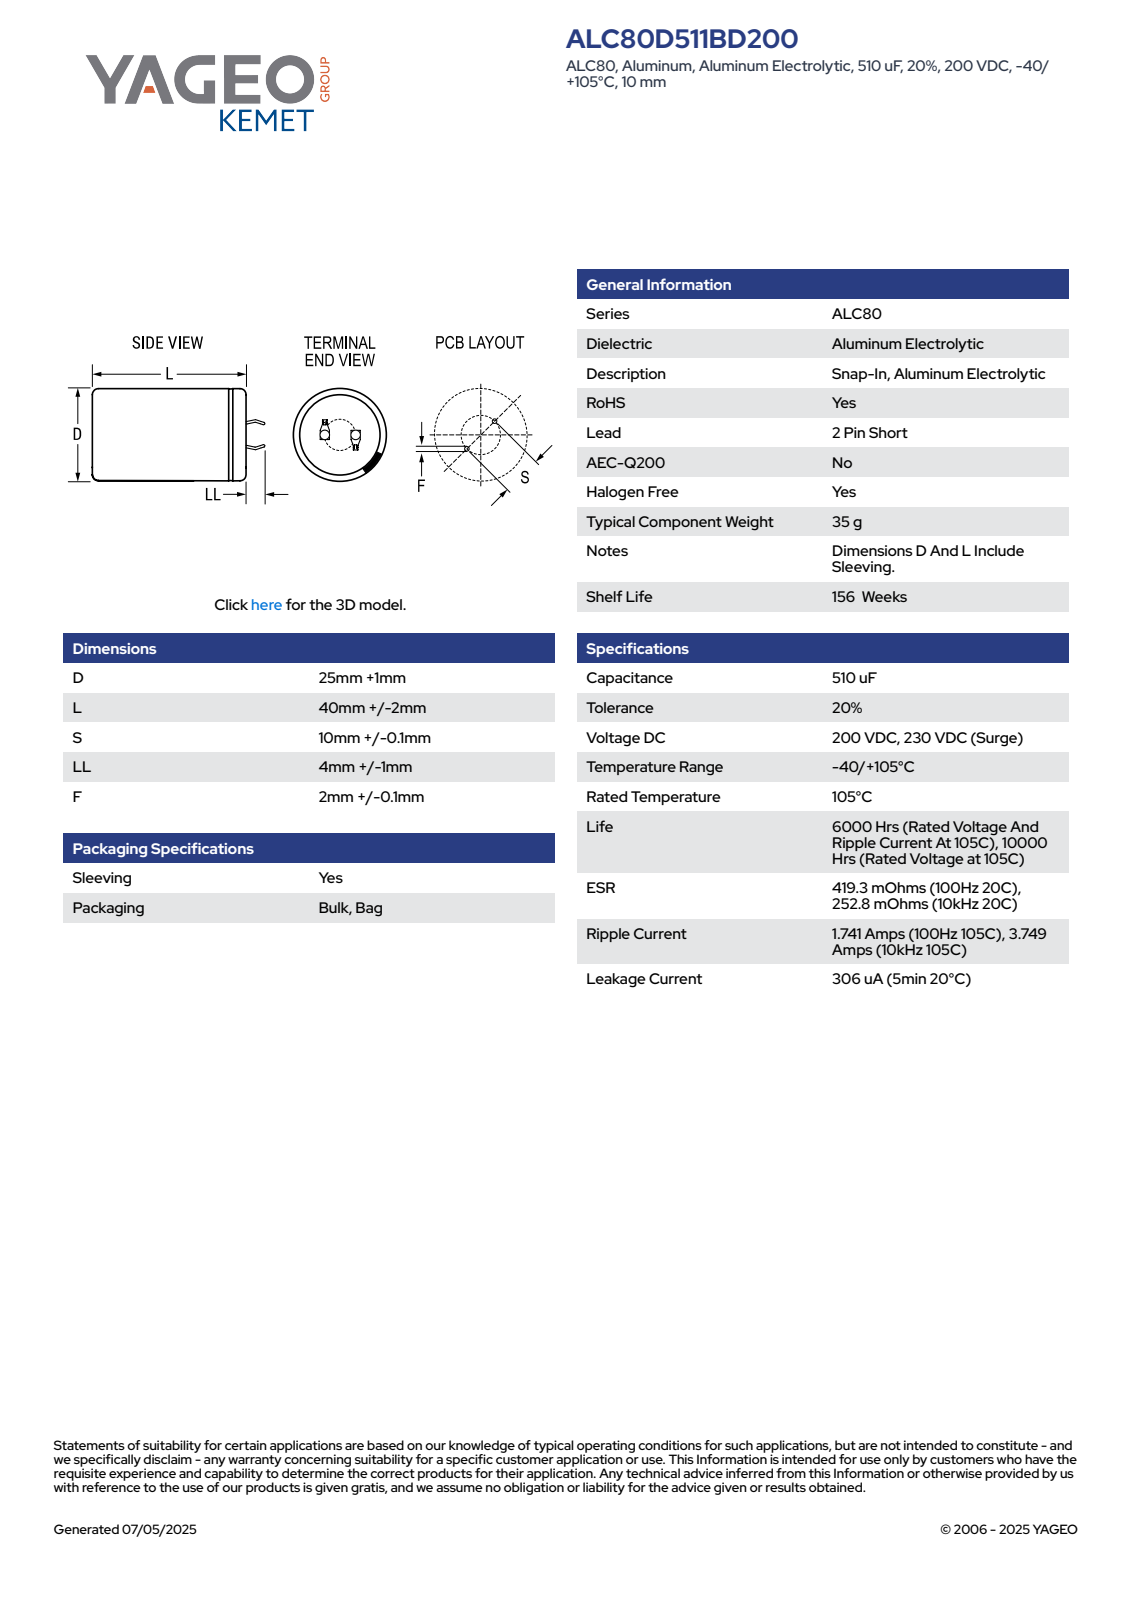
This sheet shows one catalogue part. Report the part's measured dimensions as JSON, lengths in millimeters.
{"part_name": "CARS_K2P_25X40_D26L42S10LL5F2.1", "step_written_by": "SolidWorks 2014 (AUTOMOTIVE_DESIGN)", "units": "millimeters", "bodies": {"solids": 1, "faces": 100, "planar": 52, "cylindrical": 9, "other": 39}, "overall_size": [46.99, 26, 26], "volume_mm3": 22105, "surface_area_mm2": 4503, "round_holes": [[23, 1]], "round_bosses_or_shafts": [[26, 1]], "partial_cylinders_radius": [[12.99, 1]], "face_to_face_distances": [41.99, 42.49, 0.5, 7.08, 0.6, 0.59, 7.6, 0.75, 1.35, 7.68]}
